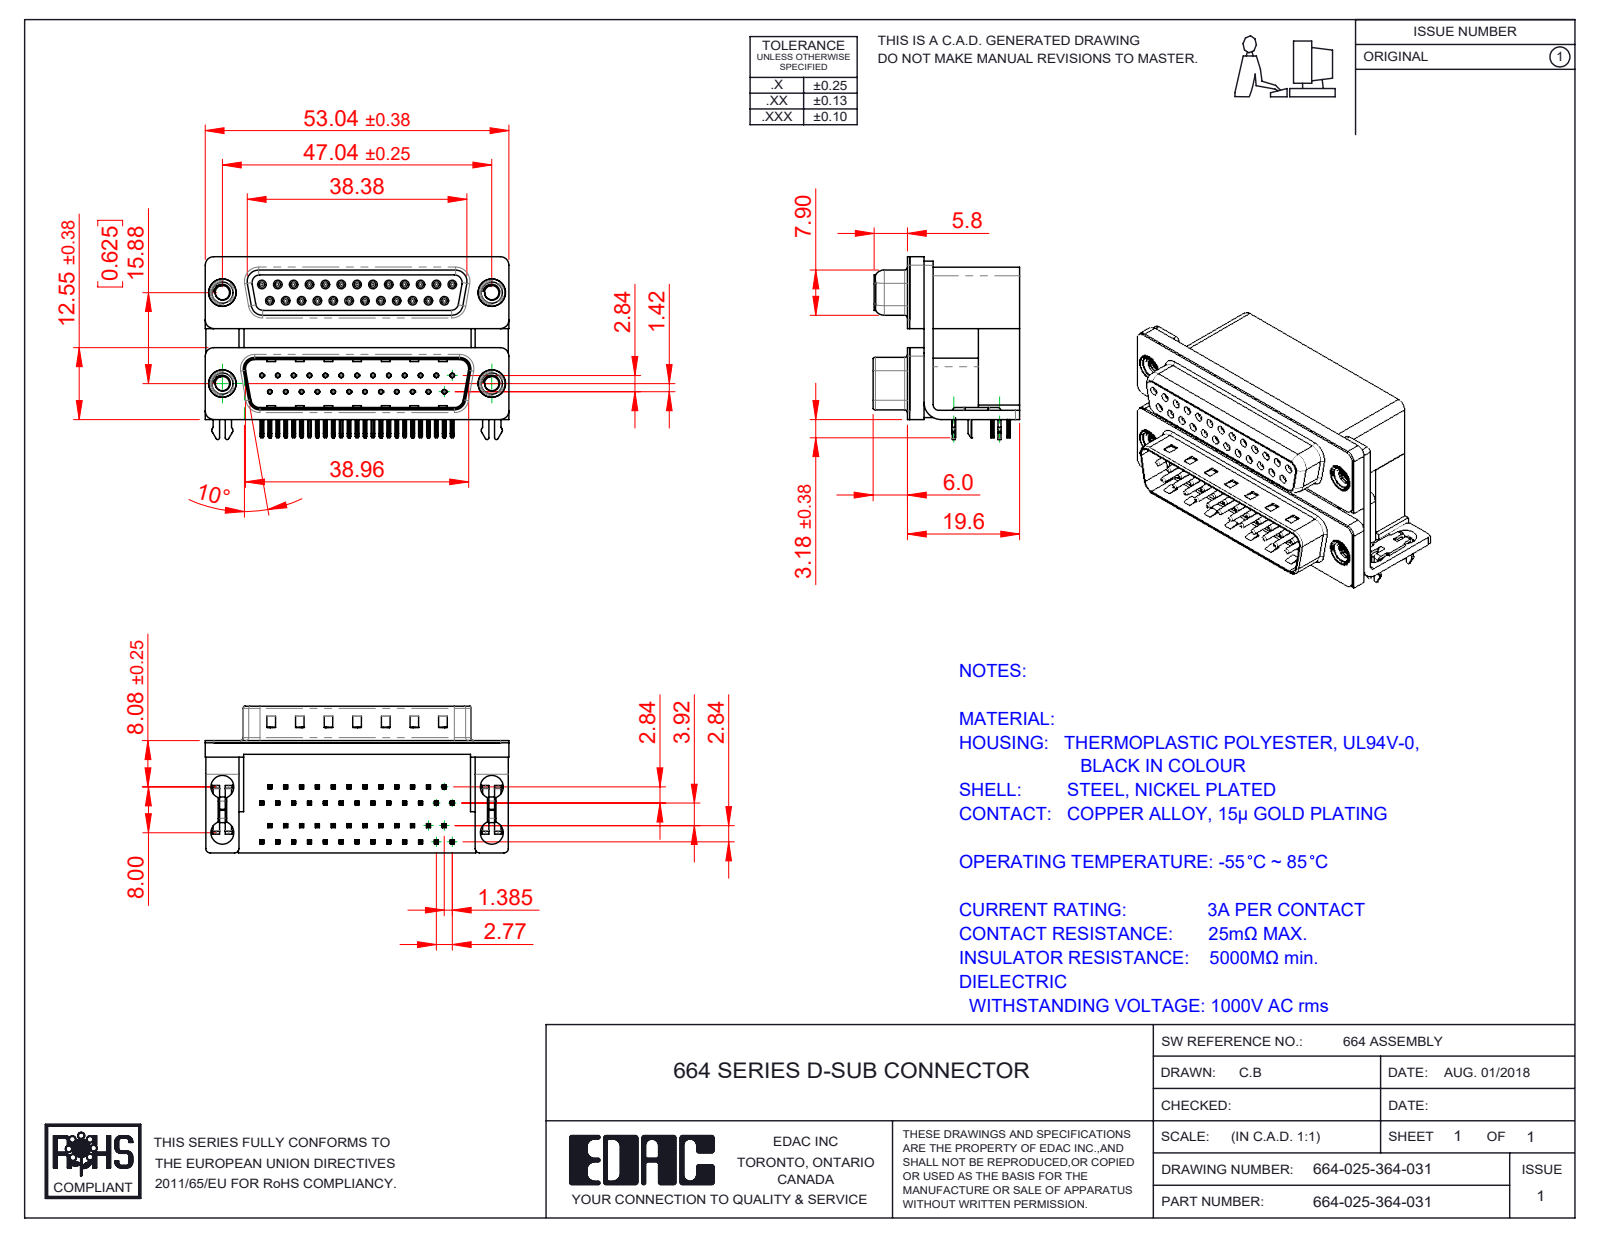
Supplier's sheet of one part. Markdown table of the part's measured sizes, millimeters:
| quantity | value |
| --- | --- |
| part name | 664 Shell Receptacle_25 Contacts; 664 Housing Lower_25 Contacts; 664-025-364-031; 664 Housing Upper_25 Contacts L (+8 more) |
| STEP written by | SolidWorks 2020 (CONFIG_CONTROL_DESIGN) |
| units | millimeters |
| bodies | 63 solids, 6359 faces (3359 planar, 1601 cylindrical, 1399 other) |
| overall size | 53.04 × 31.93 × 25.6 |
| volume | 21 538 mm³ |
| surface area | 23 451 mm² |
| round holes (diameter × count) | 0.8 × 50, 0.35 × 25, 0.9 × 25, 4 × 8, 2.5 × 4, 3.5 × 4, 4.8 × 4, 5 × 4 |
| round bosses / shafts (diameter × count) | 1.2 × 25, 0.75 × 25, 4.9 × 4, 4.75 × 4, 3.9 × 4 |
| partial cylindrical surfaces (radius × count) | 0.1 × 202, 0.25 × 110, 0.15 × 100, 0.12 × 50, 0.35 × 50, 0.34 × 25, 0.5 × 16, 1.5 × 13 |
| main face-to-face distances | 0.4, 19.2, 7.2, 12, 10.7, 16.7, 9.5, 2.5, 15.53, 26.23 |
| hole center spacings | 2.77, 3.16, 5.54, 8.31, 11.08, 13.85, 16.62, 5.03 |
